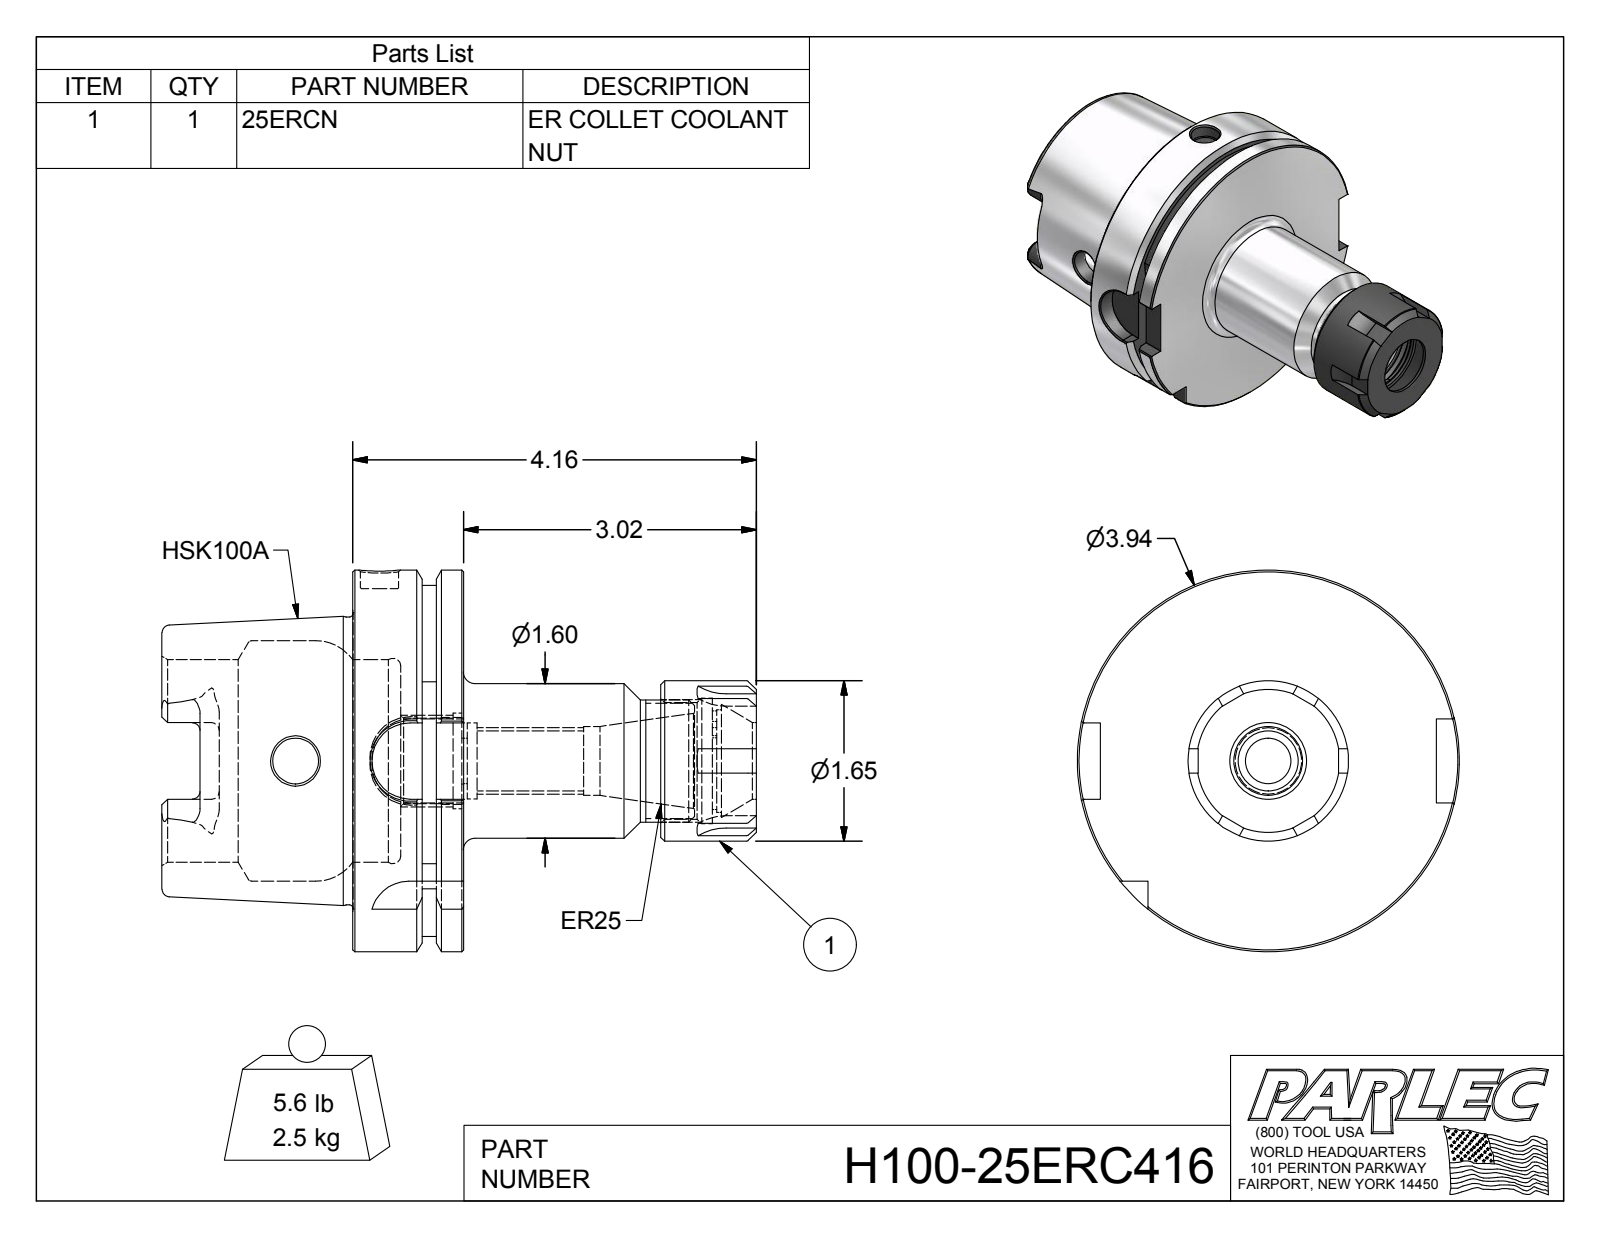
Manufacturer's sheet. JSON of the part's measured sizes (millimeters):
{"part_name": "H100-25ERC416; H100-25ER4-1; 25ERCN", "step_written_by": "Autodesk Inventor 2012 (AUTOMOTIVE_DESIGN)", "units": "millimeters", "bodies": {"solids": 2, "faces": 192, "planar": 74, "cylindrical": 53, "other": 65}, "overall_size": [155.7, 100, 100], "volume_mm3": 324600, "surface_area_mm2": 67940, "round_holes": [[12, 2], [10, 1], [12, 1], [15.7, 1], [18, 1], [19.9, 1], [20.2, 1], [22.4, 1], [25, 1], [26.8, 1], [30.5, 1], [32.9, 1]], "round_bosses_or_shafts": [[100, 1], [75.4, 1], [42, 1], [40.5, 1], [32, 1]], "partial_cylinders_radius": [[2, 6], [12.7, 6], [4.9, 4], [10, 4], [12, 1], [13.1, 1], [46, 1]], "face_to_face_distances": [29, 12.5, 16.5, 50, 62.5, 79, 155.7, 105.7, 93.2, 76.7]}
